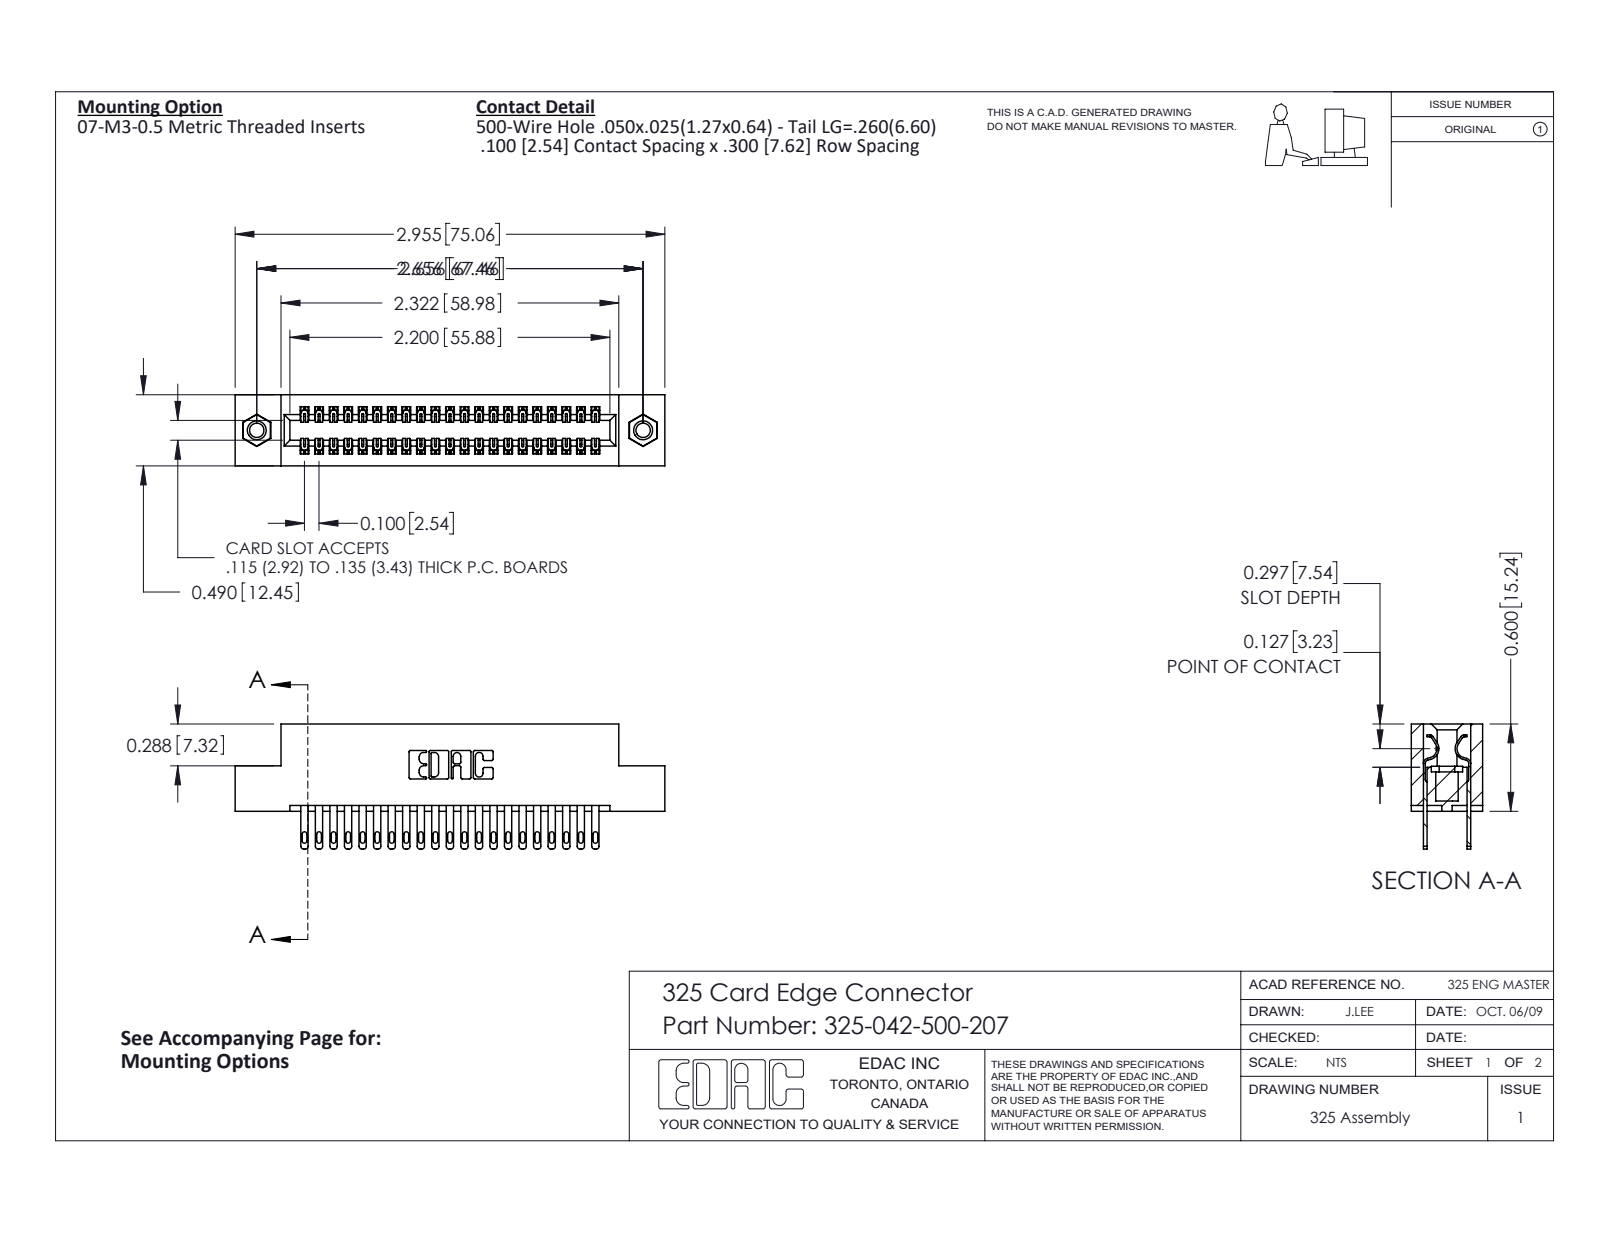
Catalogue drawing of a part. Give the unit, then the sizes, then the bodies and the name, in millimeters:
Units: millimetres
Overall size (bounding box): 75.1 × 21.8 × 12.4
Round holes (diameter × count): ⌀2.5 ×2, ⌀3.2 ×2, ⌀4.1 ×2
Round bosses / shafts (diameter × count): ⌀3.9 ×2
Partial cylindrical surfaces — rounded edges, fillets, slot ends (radius × count): R0.2 ×63, R0.4 ×42, R0.5 ×42, R0.3 ×22, R0.2 ×6, R0.8 ×6, R0.7 ×3, R0.4 ×2
Main face-to-face distances: 2.1, 10.3, 7.6, 2.7, 9.7, 0.6, 12.4, 8.3, 15.2, 1
Hole centre spacings: 67.5
Volume: 9 620 mm³ · Surface area: 11 610 mm²
Bodies: 45 solids, 2190 faces (1362 planar, 812 cylindrical, 16 other)
Part name (STEP PRODUCT): 325-292-001_325-293-100; 325 Part_TI; 345-250-001_345-250-005-103; 325-042-500-207
STEP written by: SolidWorks 2016 (CONFIG_CONTROL_DESIGN)
